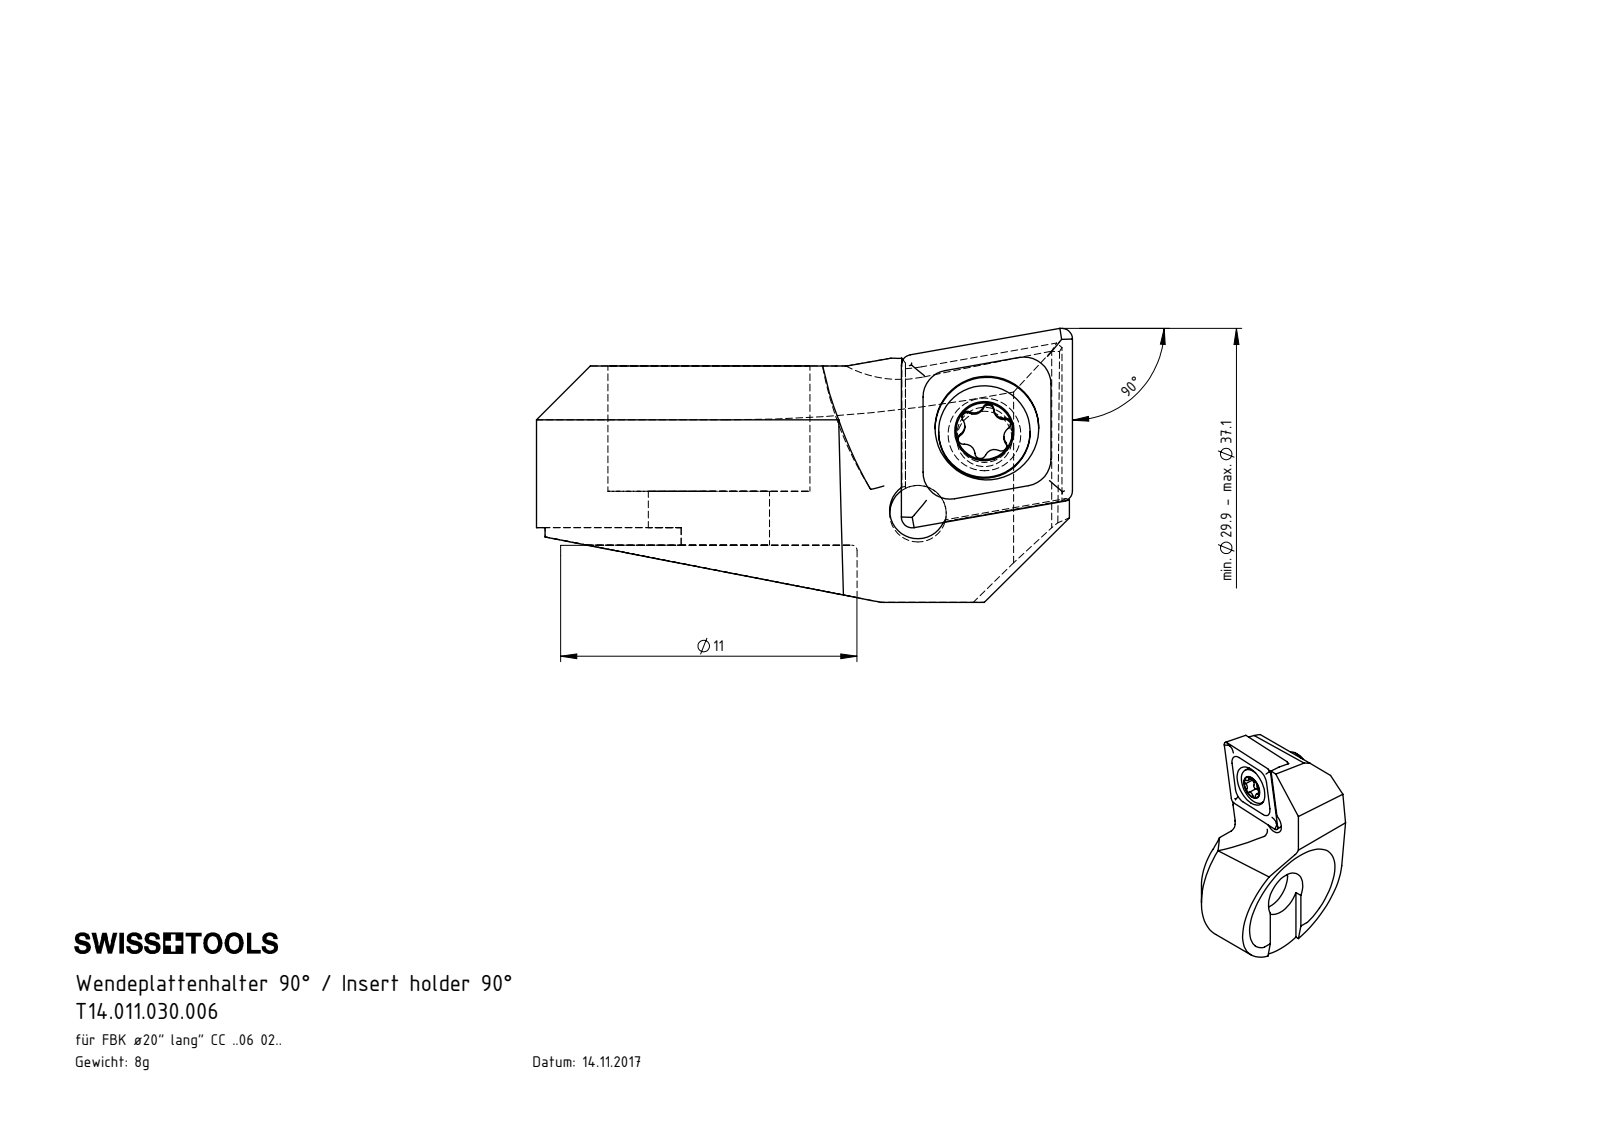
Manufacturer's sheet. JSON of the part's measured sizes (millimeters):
{"part_name": "F20.WCA.001.008; F20-WCA.001.008_D_fertigbearbeitet; WCA-ER2.001.006_A; CCMT060204", "step_written_by": "SolidWorks 2017 (AUTOMOTIVE_DESIGN)", "units": "millimeters", "bodies": {"solids": 3, "faces": 104, "planar": 39, "cylindrical": 27, "other": 38}, "overall_size": [19.9, 12.8, 10.17], "volume_mm3": 914, "surface_area_mm2": 1073, "round_holes": [[2.05, 1], [2.1, 1], [2.8, 1], [3.85, 1], [4.5, 1], [7.5, 1]], "round_bosses_or_shafts": [[3.4, 1], [2.5, 1]], "partial_cylinders_radius": [[0.21, 6], [0.36, 5], [0.5, 2], [0.36, 1], [5, 1], [5.5, 1], [6.4, 1], [10, 1]], "face_to_face_distances": [2, 2.28, 4.65, 6.65, 8.77, 4.12, 2.12, 6, 2.77, 1.35], "hole_center_spacings": [3.84, 4]}
